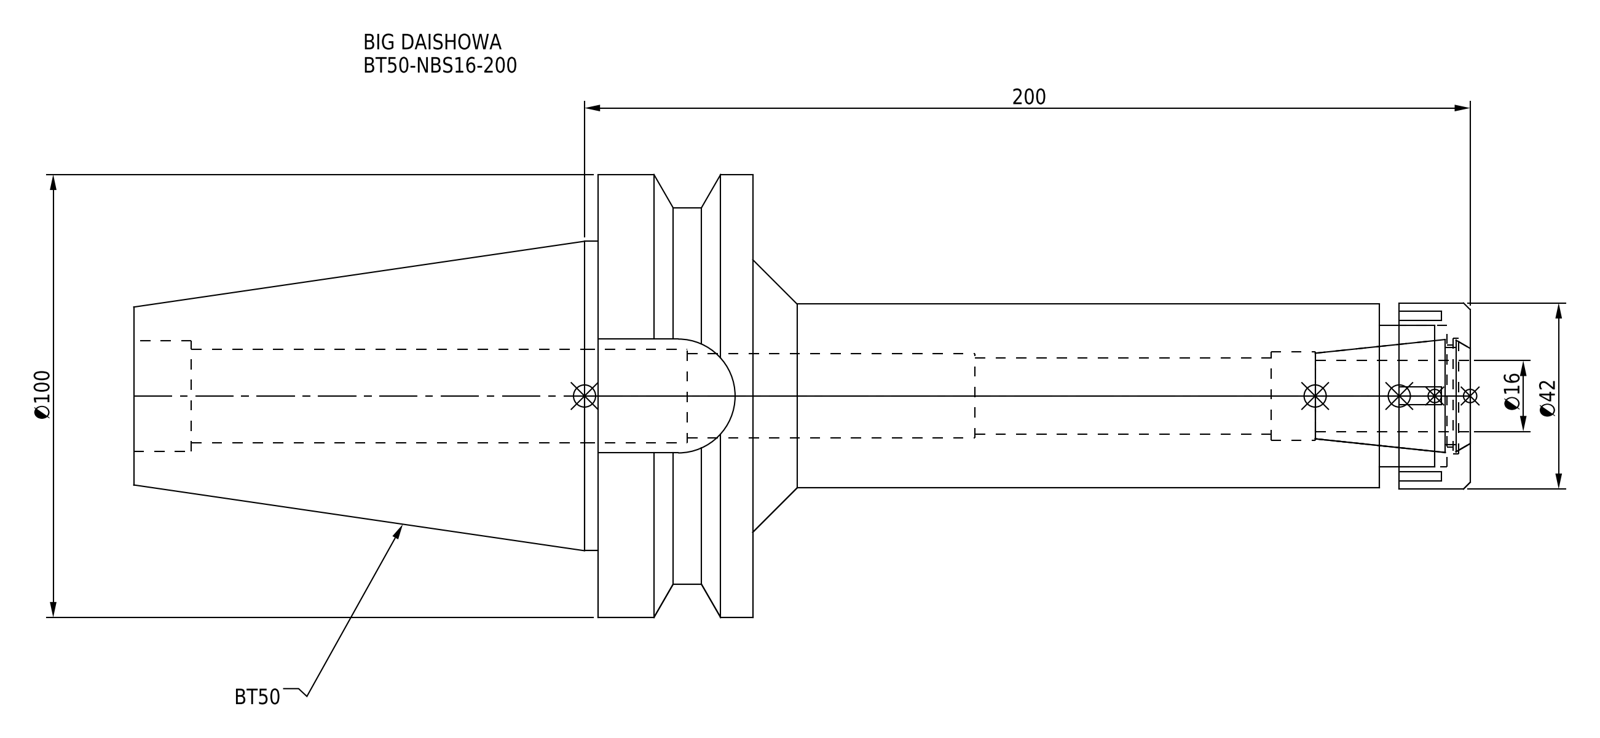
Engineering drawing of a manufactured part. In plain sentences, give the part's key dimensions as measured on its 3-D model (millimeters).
The part is named "BT50-NBS16-200; BT50-NBS16-200.stp; BT50-NBS16-200_1.stp; BT50NB16200-160_ASM.stp (+3 more)". Its 3-D file was written by "SolidWorks 2019 (CONFIG_CONTROL_DESIGN)". It is 2 solids with 93 faces: 45 planar, 34 cylindrical and 14 other. Overall it measures 301.8 by 100 by 100 millimeters. Its volume is 619 862 cubic millimeters and its surface area 88 026 square millimeters. Round holes: 1 of diameter 17.3, 1 of diameter 19, 1 of diameter 20, 1 of diameter 21.2, 1 of diameter 23, 1 of diameter 25, 1 of diameter 26, 1 of diameter 32. Round bosses or shafts: 1 of diameter 100, 1 of diameter 85, 1 of diameter 69.85, 1 of diameter 42, 1 of diameter 41.5. Partial cylindrical surfaces (rounded edges, fillets, slot ends): 1 of radius 12.85. The main face-to-face distances are 35, 162, 197, 301.8, 139.8, 104.8, 70.8, 8, 20.5, 141.5.
